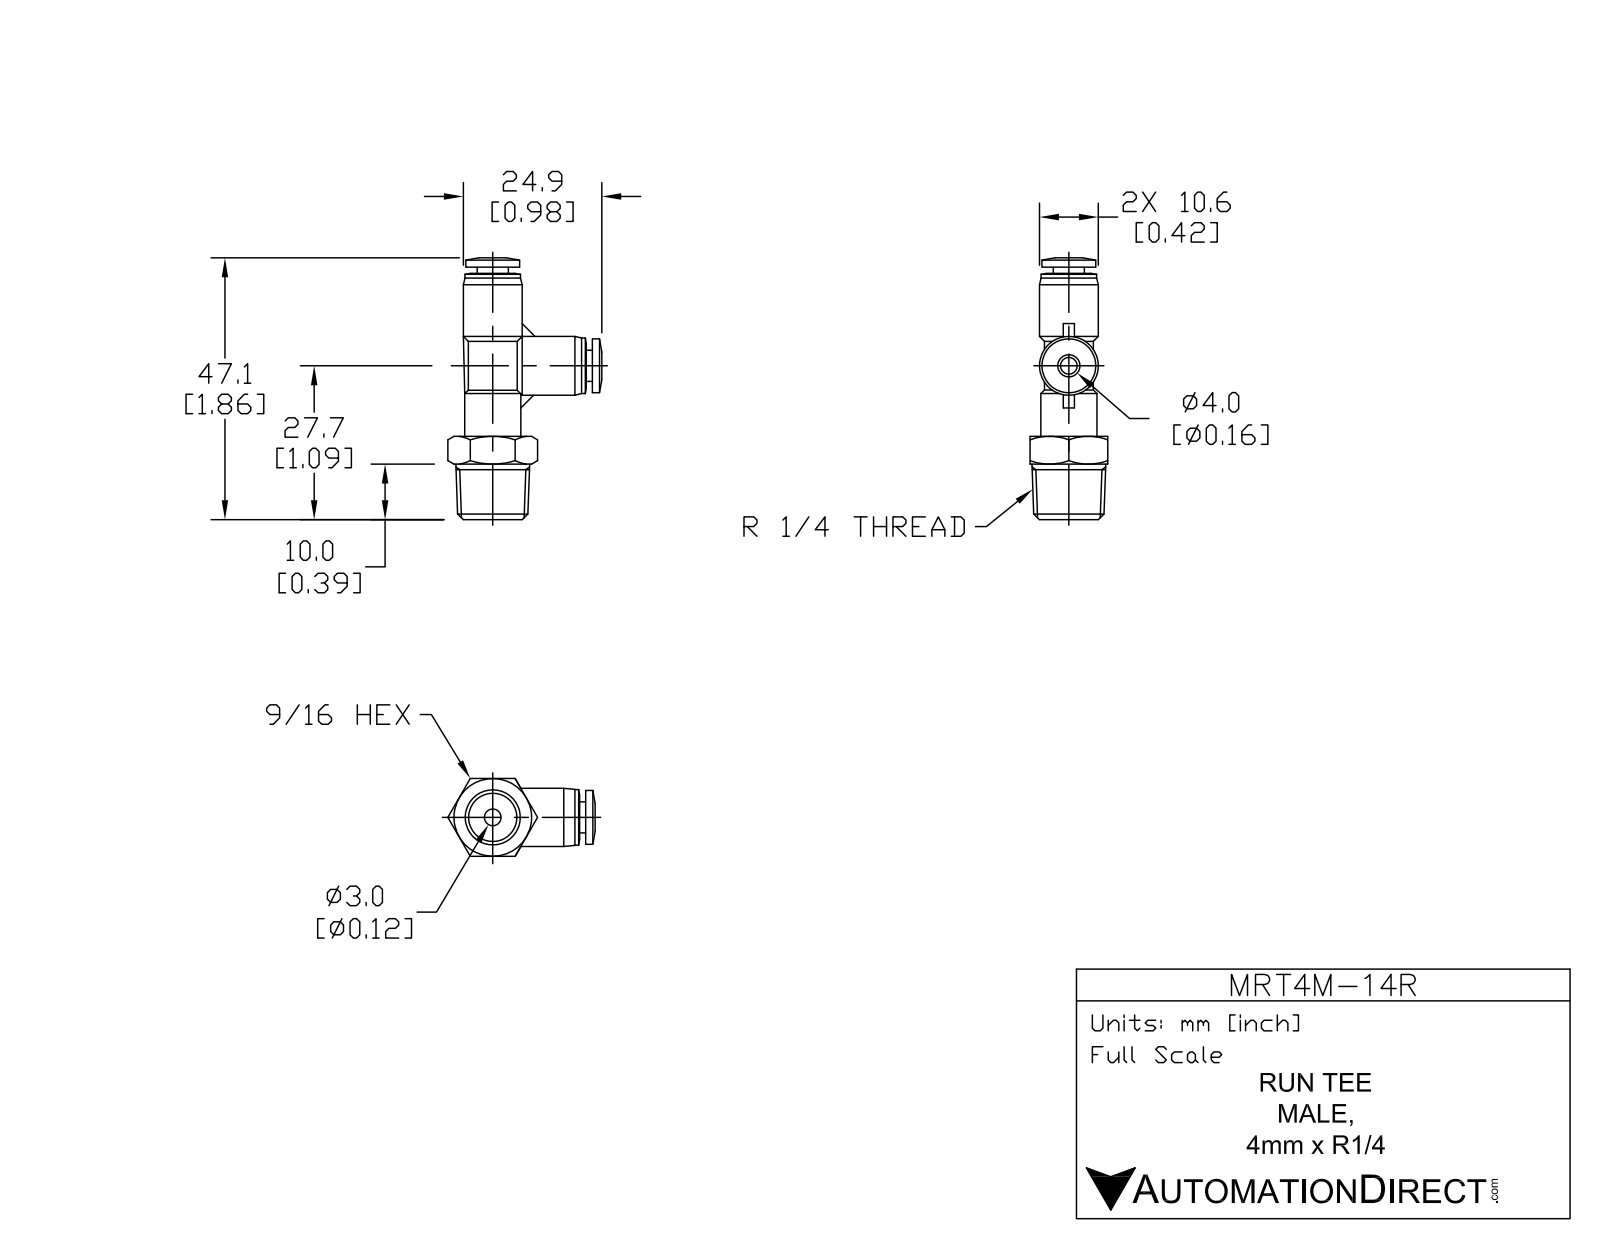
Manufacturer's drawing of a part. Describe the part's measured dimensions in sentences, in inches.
The part is named "MRT4M-14R". Its 3-D file was written by "SolidWorks 2015 (AUTOMOTIVE_DESIGN)". It is 1 solid with 100 faces: 25 planar, 32 cylindrical and 43 other. Overall it measures 1.848 by 1.084 by 0.551 inches. Its volume is 0.311 cubic inches and its surface area 5.188 square inches. Round holes: 2 of diameter 0.118, 2 of diameter 0.169. Round bosses or shafts: 2 of diameter 0.417, 2 of diameter 0.394, 2 of diameter 0.382, 2 of diameter 0.346, 2 of diameter 0.22, 1 of diameter 0.398. The main face-to-face distances are 0.551, 0.591, 0.043, 1.781, 1.191, 0.236, 0.315, 1.738, 1.148, 0.394.
